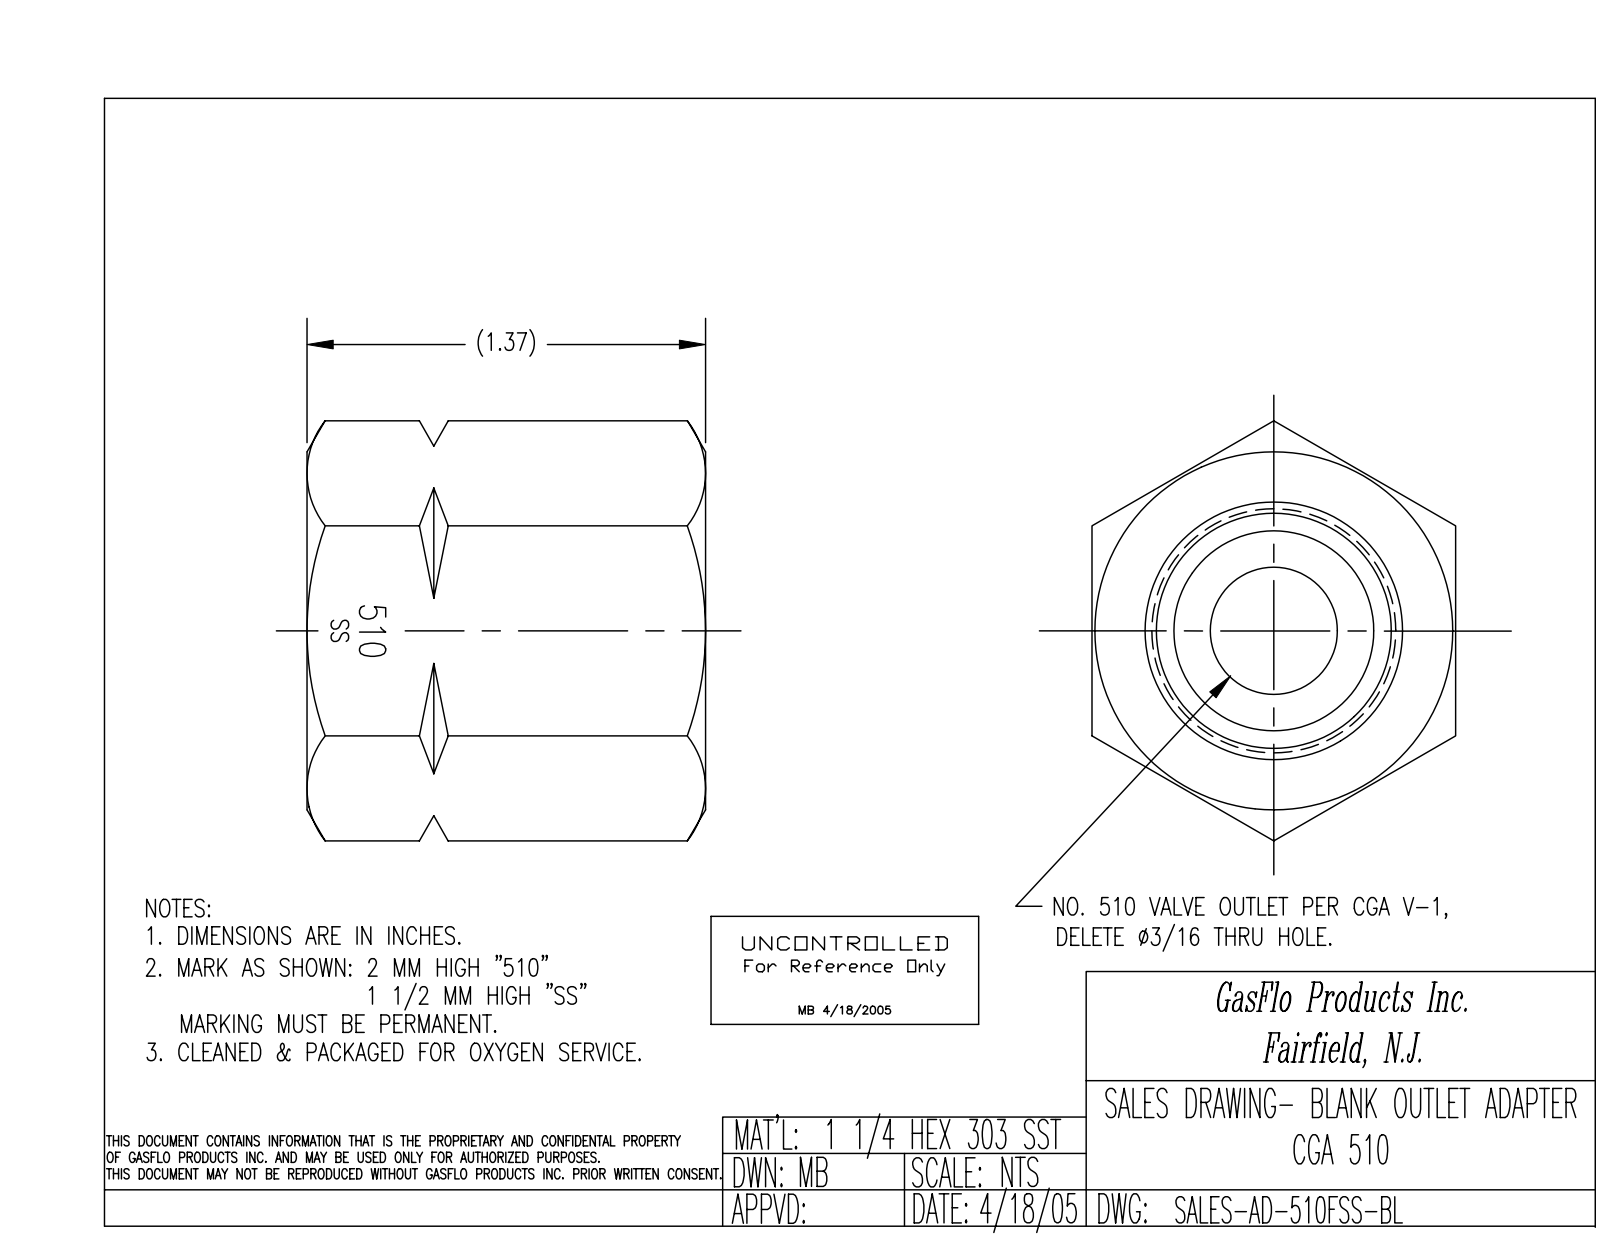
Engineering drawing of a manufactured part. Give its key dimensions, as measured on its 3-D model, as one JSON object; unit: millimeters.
{"part_name": "AD-510FSS-BL", "step_written_by": "SolidWorks 2018 (CONFIG_CONTROL_DESIGN)", "units": "millimeters", "bodies": {"solids": 1, "faces": 124, "planar": 31, "cylindrical": 18, "other": 75}, "overall_size": [36.7, 34.8, 31.8], "volume_mm3": 22680, "surface_area_mm2": 7600, "round_holes": [[10.7, 1], [20.6, 1]], "face_to_face_distances": [31.8, 31.8, 34.8, 17.3, 17.4, 31.5, 7.5, 9.9, 27.3, 7.2]}
